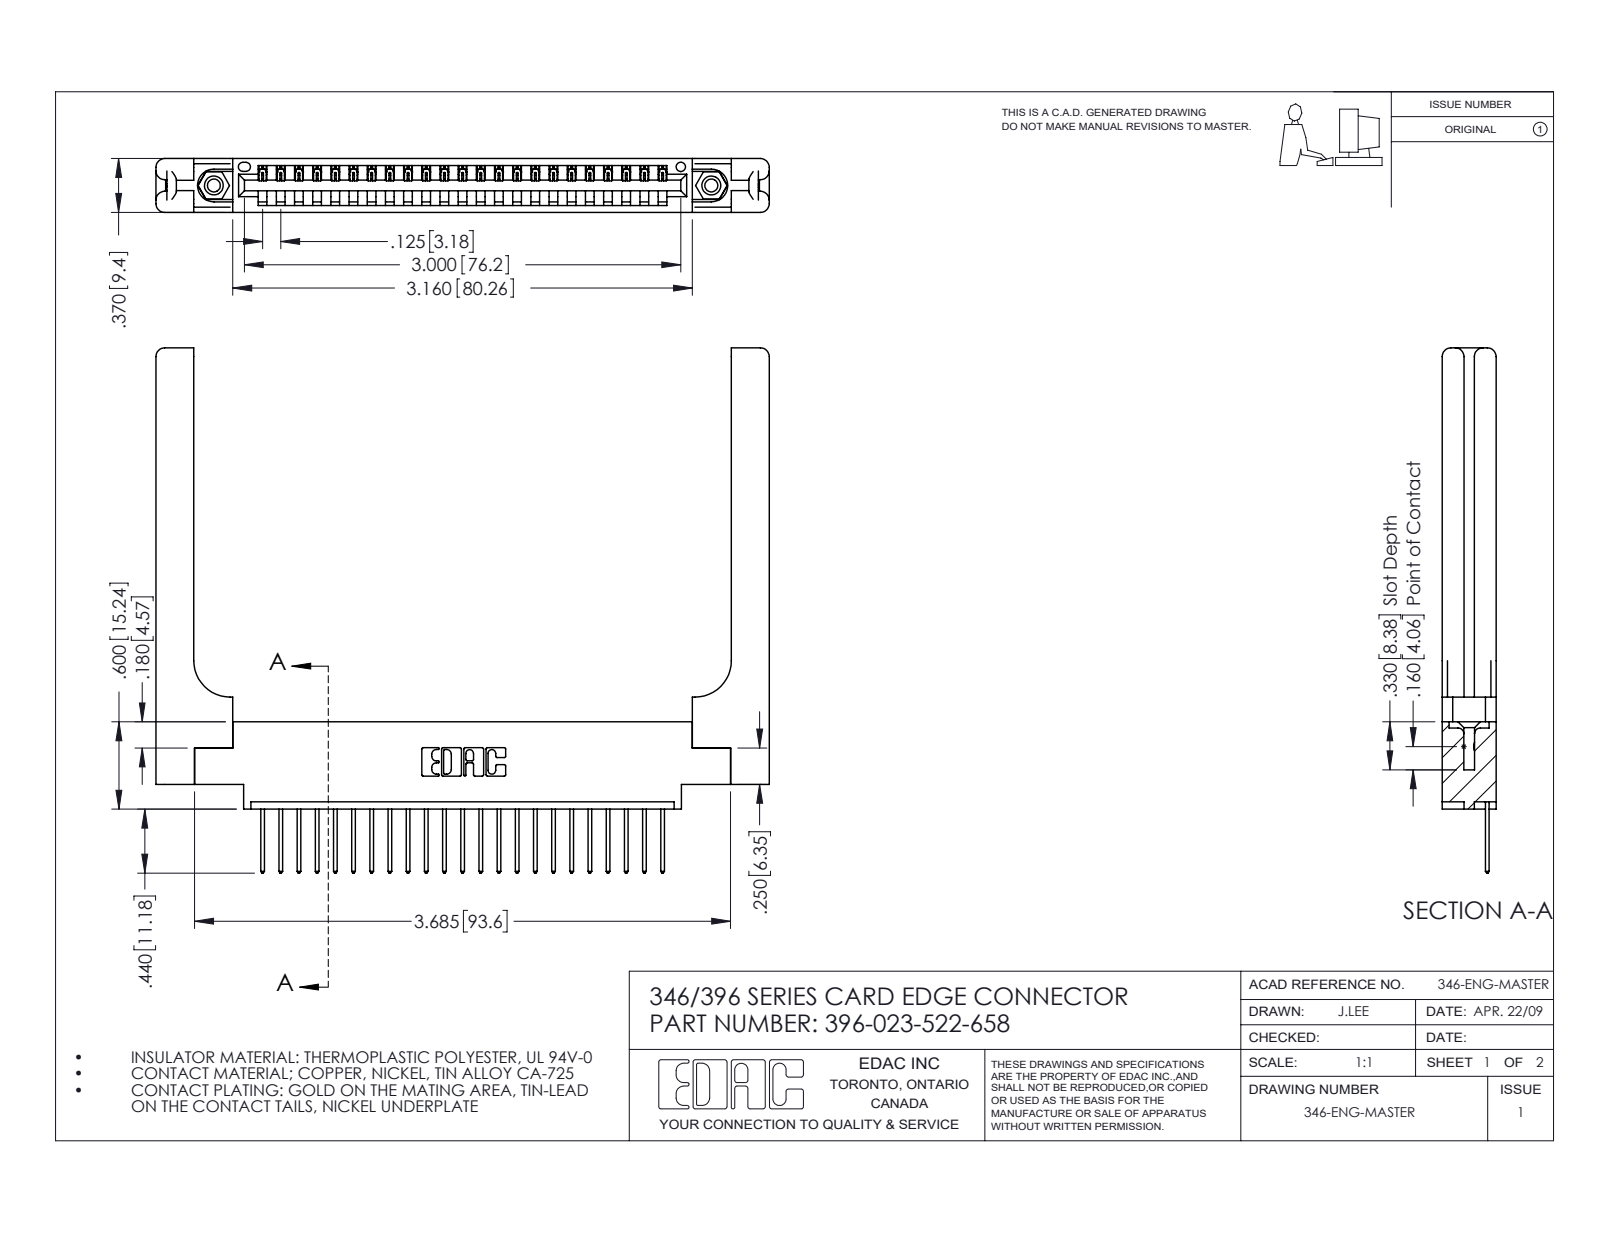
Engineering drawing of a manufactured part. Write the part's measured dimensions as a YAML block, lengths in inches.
part_name: "346-220-058_345-220-058; 345-250-001_345-250-001-102; 345-292-001_345-293-122; 346 Part_0.170 Offset - 0.156 Dia-TH (+1 more)"
step_written_by: "SolidWorks 2016 (CONFIG_CONTROL_DESIGN)"
units: inches
bodies: {solids: 28, faces: 1716, planar: 1148, cylindrical: 508, other: 60}
overall_size: [4.216, 3.61, 0.37]
volume: 1.067
surface_area: 27.39
round_holes:
  - {diameter: 0.089, count: 2}
  - {diameter: 0.125, count: 2}
  - {diameter: 0.156, count: 2}
  - {diameter: 0.064, count: 1}
round_bosses_or_shafts:
  - {diameter: 0.155, count: 2}
partial_cylinders:
  - {radius: 0.006, count: 46}
  - {radius: 0.01, count: 46}
  - {radius: 0.01, count: 22}
  - {radius: 0.06, count: 16}
  - {radius: 0.007, count: 6}
  - {radius: 0.031, count: 6}
  - {radius: 0.026, count: 3}
  - {radius: 0.03, count: 2}
face_to_face_distances: [0.37, 0.072, 0.048, 0.322, 0.15, 0.148, 0.25, 0.298, 0.025, 0.102]
hole_center_spacings: [0.246, 3.212, 3.42]
